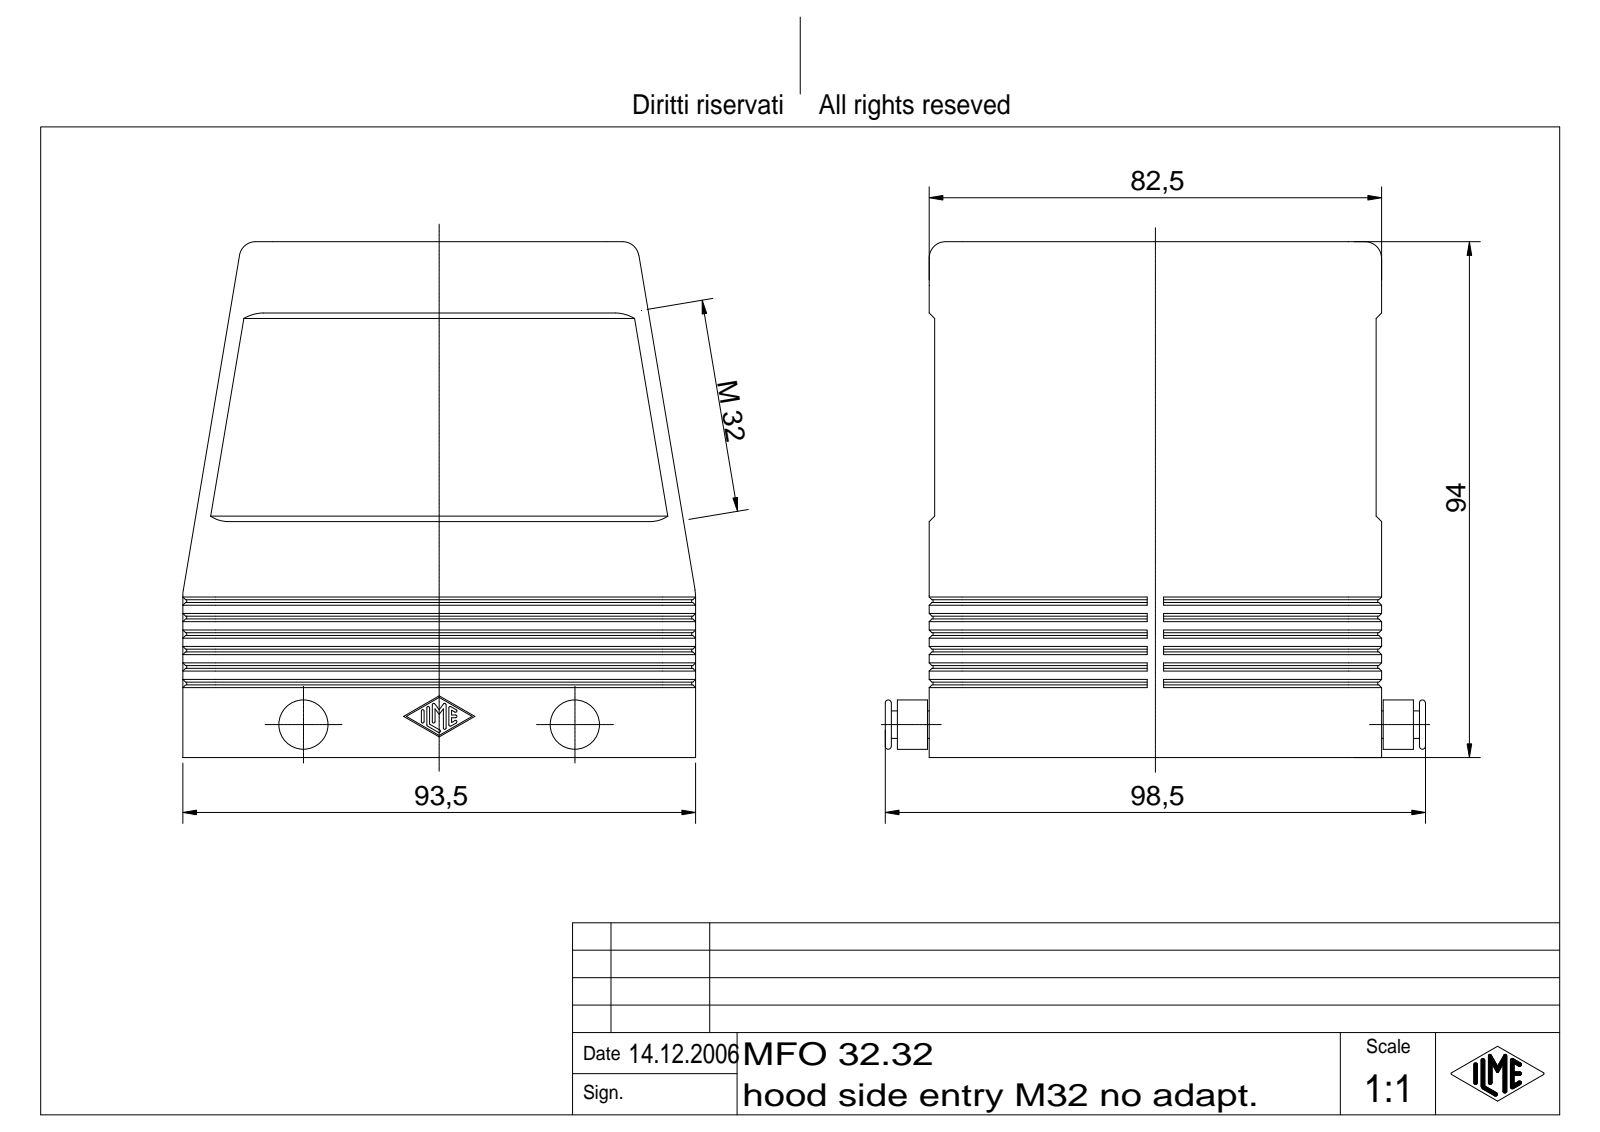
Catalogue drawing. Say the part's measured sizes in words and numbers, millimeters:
The part is named "MFO 32.32". Its 3-D file was written by "Autodesk Inventor 7 (AUTOMOTIVE_DESIGN)". It is 1 solid with 601 faces: 207 planar, 152 cylindrical and 242 other. Overall it measures 98.5 by 94 by 93.5 millimeters. Its volume is 142 875 cubic millimeters and its surface area 73 909 square millimeters. Round holes: 4 of diameter 2.46, 4 of diameter 3.5, 1 of diameter 39. Round bosses or shafts: 2 of diameter 9, 2 of diameter 5. Partial cylindrical surfaces (rounded edges, fillets, slot ends): 14 of radius 0.25, 12 of radius 2, 10 of radius 6, 4 of radius 3, 2 of radius 5.3. The main face-to-face distances are 4, 78.5, 74.5, 82.5, 3, 11, 1, 77.5, 81.5, 71.5. The hole center spacings are 27, 77.5, 82.07.
